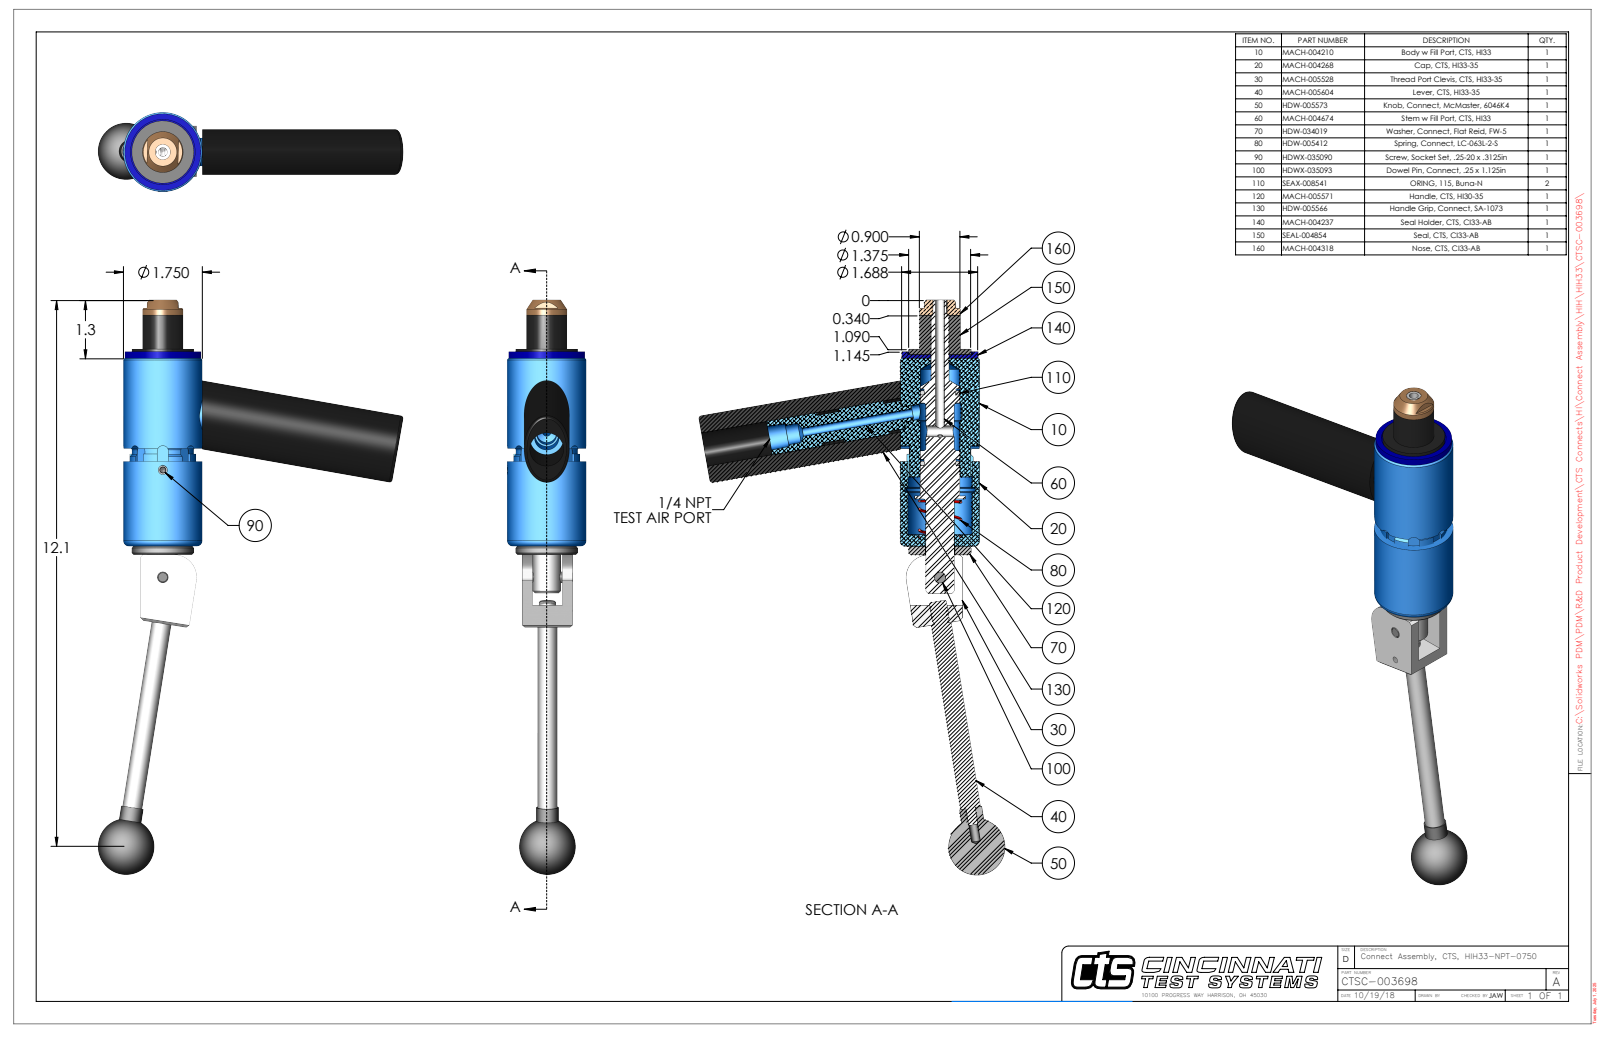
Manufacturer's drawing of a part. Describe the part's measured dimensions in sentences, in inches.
The part is named "CTSC-003698". Its 3-D file was written by "SolidWorks 2023 (AUTOMOTIVE_DESIGN)". It is 10 solids with 321 faces: 118 planar, 138 cylindrical and 65 other. Overall it measures 12.729 by 6.763 by 1.75 inches. Its volume is 18.33 cubic inches and its surface area 116.5 square inches. Round holes: 2 of diameter 0.201, 2 of diameter 0.313, 1 of diameter 0.15, 1 of diameter 0.187, 1 of diameter 0.204, 1 of diameter 0.249, 1 of diameter 0.25, 1 of diameter 0.251, 1 of diameter 0.39, 1 of diameter 0.397, 1 of diameter 0.403, 1 of diameter 0.438. Round bosses or shafts: 2 of diameter 0.312, 2 of diameter 0.25, 1 of diameter 1.75, 1 of diameter 1.687, 1 of diameter 1.38, 1 of diameter 1.375, 1 of diameter 0.9, 1 of diameter 0.75. Partial cylindrical surfaces (rounded edges, fillets, slot ends): 4 of radius 0.125, 2 of radius 0.029, 1 of radius 0.143, 1 of radius 0.33, 1 of radius 0.5, 1 of radius 0.695, 1 of radius 0.709, 1 of radius 0.744. The main face-to-face distances are 0.082, 4.244, 4.162, 1.12, 4.432, 4.35, 0.188, 0.232, 0.888, 0.232. The hole center spacings are 0.74, 2.376, 3.116.
